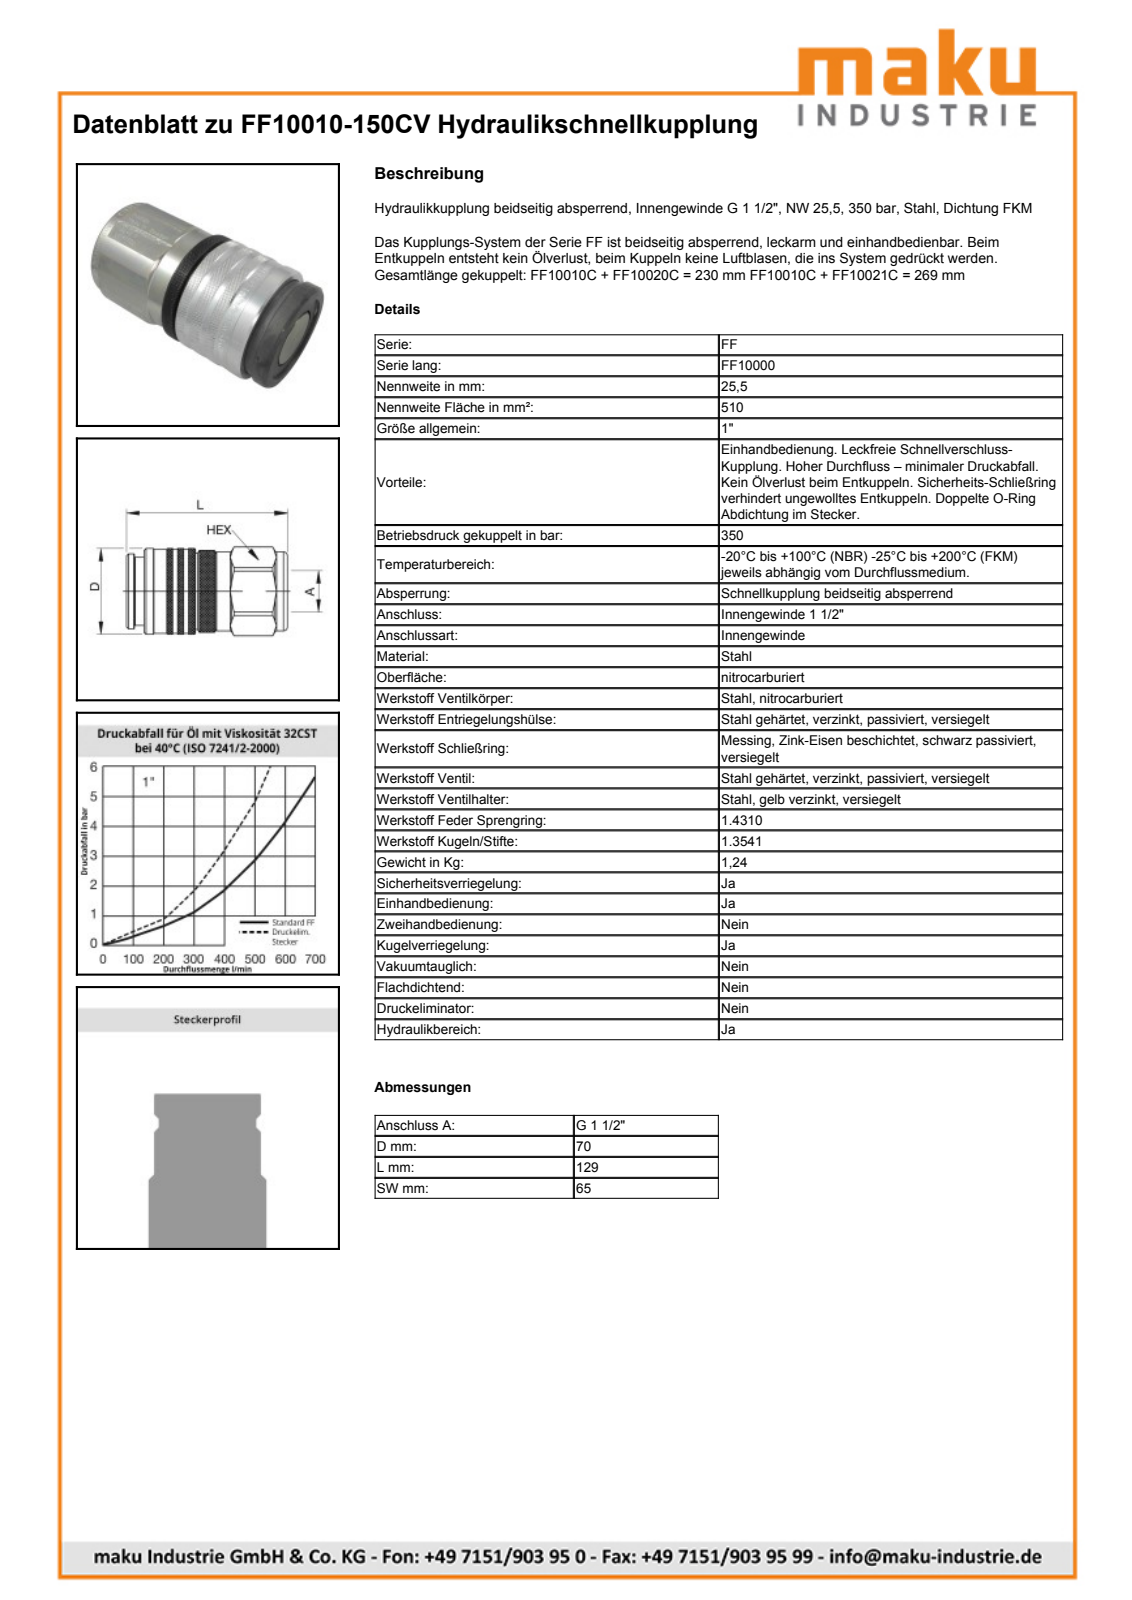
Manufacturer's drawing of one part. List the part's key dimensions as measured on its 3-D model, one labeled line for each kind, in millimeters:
Part name (STEP PRODUCT): FF10010-150CV
STEP written by: SolidWorks 2009 (AUTOMOTIVE_DESIGN)
Units: millimetres
Bodies: 1 solid, 706 faces (330 planar, 131 cylindrical, 245 other)
Overall size (bounding box): 128.8 × 70 × 70
Volume: 414 003 mm³ · Surface area: 41 966 mm²
Round holes (diameter × count): ⌀33 ×1, ⌀35.5 ×1, ⌀44.85 ×1, ⌀50 ×1, ⌀60.3 ×1
Round bosses / shafts (diameter × count): ⌀70 ×1, ⌀69.5 ×1, ⌀68.5 ×1, ⌀67.35 ×1, ⌀65 ×1, ⌀60 ×1, ⌀49.8 ×1, ⌀35 ×1
Partial cylindrical surfaces — rounded edges, fillets, slot ends (radius × count): R32.4 ×1
Main face-to-face distances: 65, 26.96, 127.25, 100.29, 128.8, 101.84, 1.55, 127.3, 100.34, 1.5
